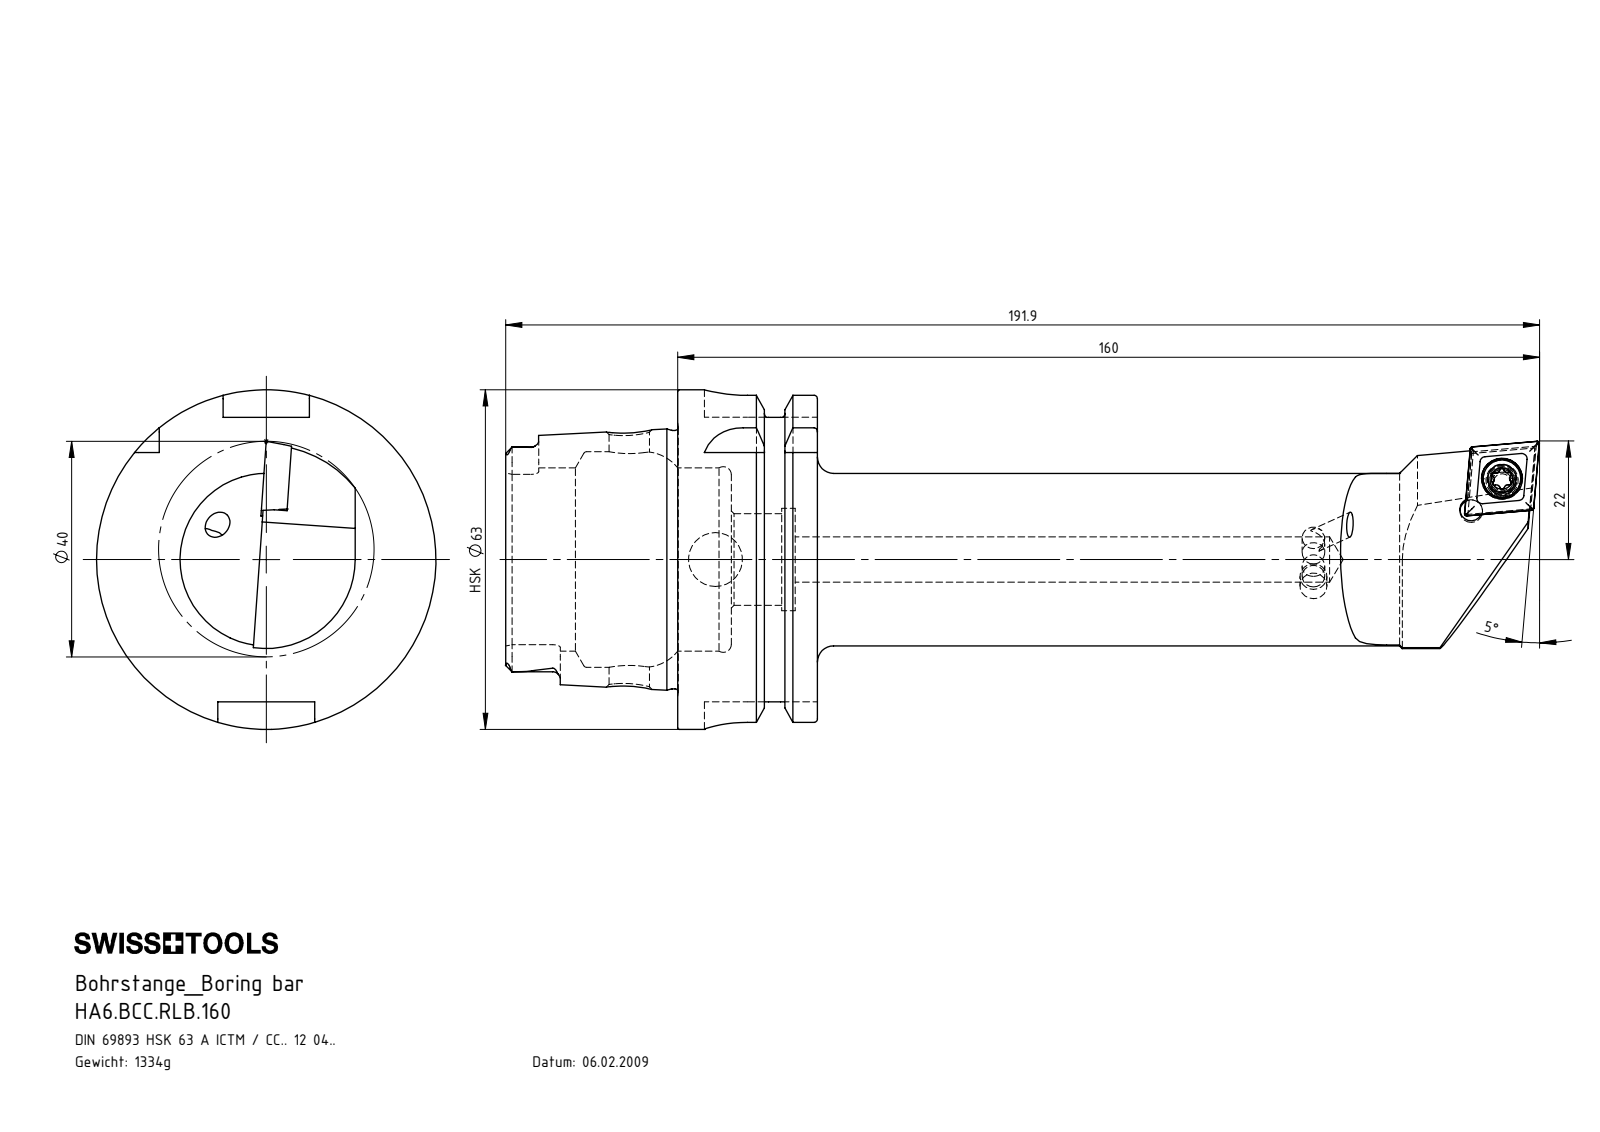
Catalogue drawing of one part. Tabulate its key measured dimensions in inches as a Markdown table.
| quantity | value |
| --- | --- |
| part name | WCC-ER2.001.010_A; CCMT120404; HA6.BCC.RLB.160; HA6-BCC.RLB.160_B |
| STEP written by | SolidWorks 2017 (AUTOMOTIVE_DESIGN) |
| units | inches |
| bodies | 3 solids, 208 faces (73 planar, 56 cylindrical, 79 other) |
| overall size | 7.554 × 2.48 × 2.48 |
| volume | 10.38 in³ |
| surface area | 59.73 in² |
| round holes (diameter × count) | 0.165 × 4, 0.197 × 1, 0.217 × 1, 0.295 × 1, 0.299 × 1, 0.331 × 1, 0.394 × 1, 0.669 × 1, 0.748 × 1, 1.339 × 1, 1.575 × 1 |
| round bosses / shafts (diameter × count) | 2.48 × 1, 2.163 × 1, 1.887 × 1, 1.26 × 1, 0.276 × 1, 0.197 × 1 |
| partial cylindrical surfaces (radius × count) | 0.015 × 6, 0.055 × 6, 0.315 × 4, 0.027 × 3, 0.027 × 3, 0.111 × 2, 0.113 × 2, 0.118 × 1 |
| main face-to-face distances | 1.022, 0.63, 0.392, 1.256, 1.648, 2.278, 2.079, 0.858, 0.467, 2.114 |
| hole center spacings | 0.315, 0.319 |
